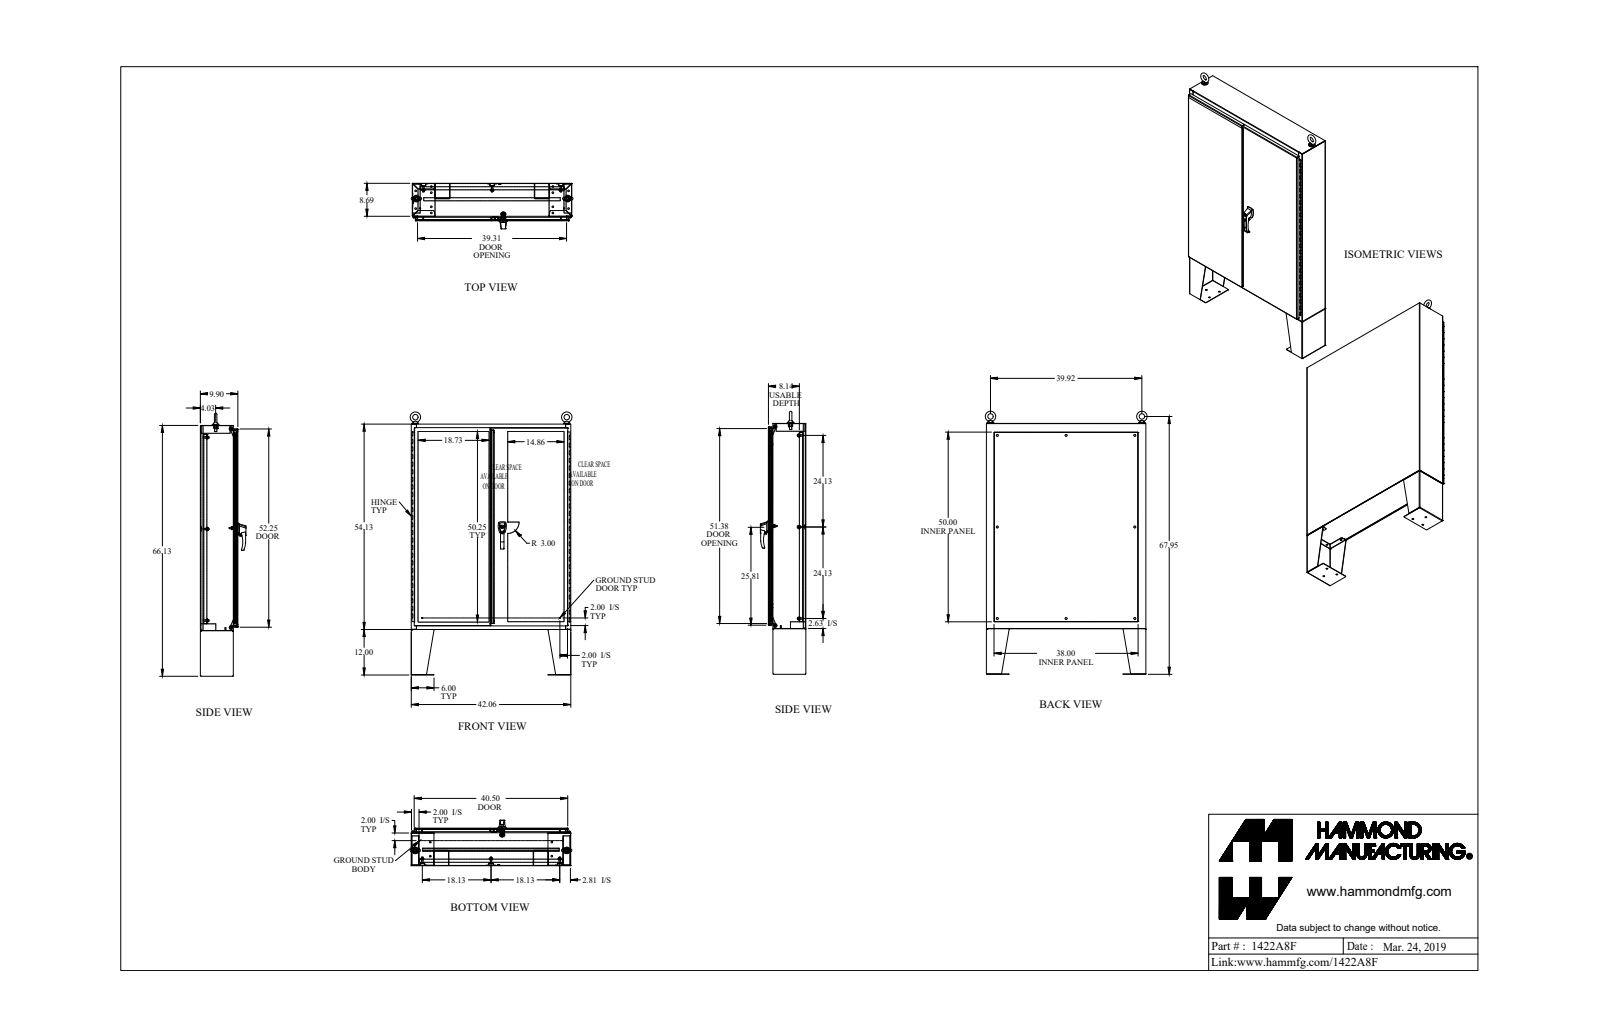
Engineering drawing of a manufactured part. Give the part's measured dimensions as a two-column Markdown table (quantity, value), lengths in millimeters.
| quantity | value |
| --- | --- |
| part name | 1422A8F_Default |
| STEP written by | SolidWorks 2019 (CONFIG_CONTROL_DESIGN) |
| units | millimeters |
| bodies | 90 solids, 2673 faces (1246 planar, 1180 cylindrical, 247 other) |
| overall size | 1772.4 × 1096.4 × 305.1 |
| volume | 15 220 000 mm³ |
| surface area | 13 950 000 mm² |
| round holes (diameter × count) | 7.7 × 18, 11.1 × 14, 7.8 × 9, 11.3 × 8, 14.3 × 8, 2.8 × 2, 6.4 × 2, 6.5 × 2, 7.1 × 2, 7.1 × 2, 8 × 2, 9.9 × 2 |
| round bosses / shafts (diameter × count) | 25.4 × 10, 16.5 × 8, 9.5 × 8, 8.4 × 8, 7.1 × 6, 6.4 × 4, 44.5 × 2, 38.1 × 2 |
| partial cylindrical surfaces (radius × count) | 1.2 × 30, 3.6 × 30, 3.2 × 22, 0.5 × 16, 0.9 × 14, 2.7 × 14, 2.9 × 12, 1.5 × 10 |
| main face-to-face distances | 1.8, 2.4, 207.5, 247.1, 249, 249.6, 251.4, 205.1, 42.1, 43.9 |
| hole center spacings | 152.4, 1037.2, 304.8, 1070.3, 457.2, 1123.2, 609.6, 1193.4 |
